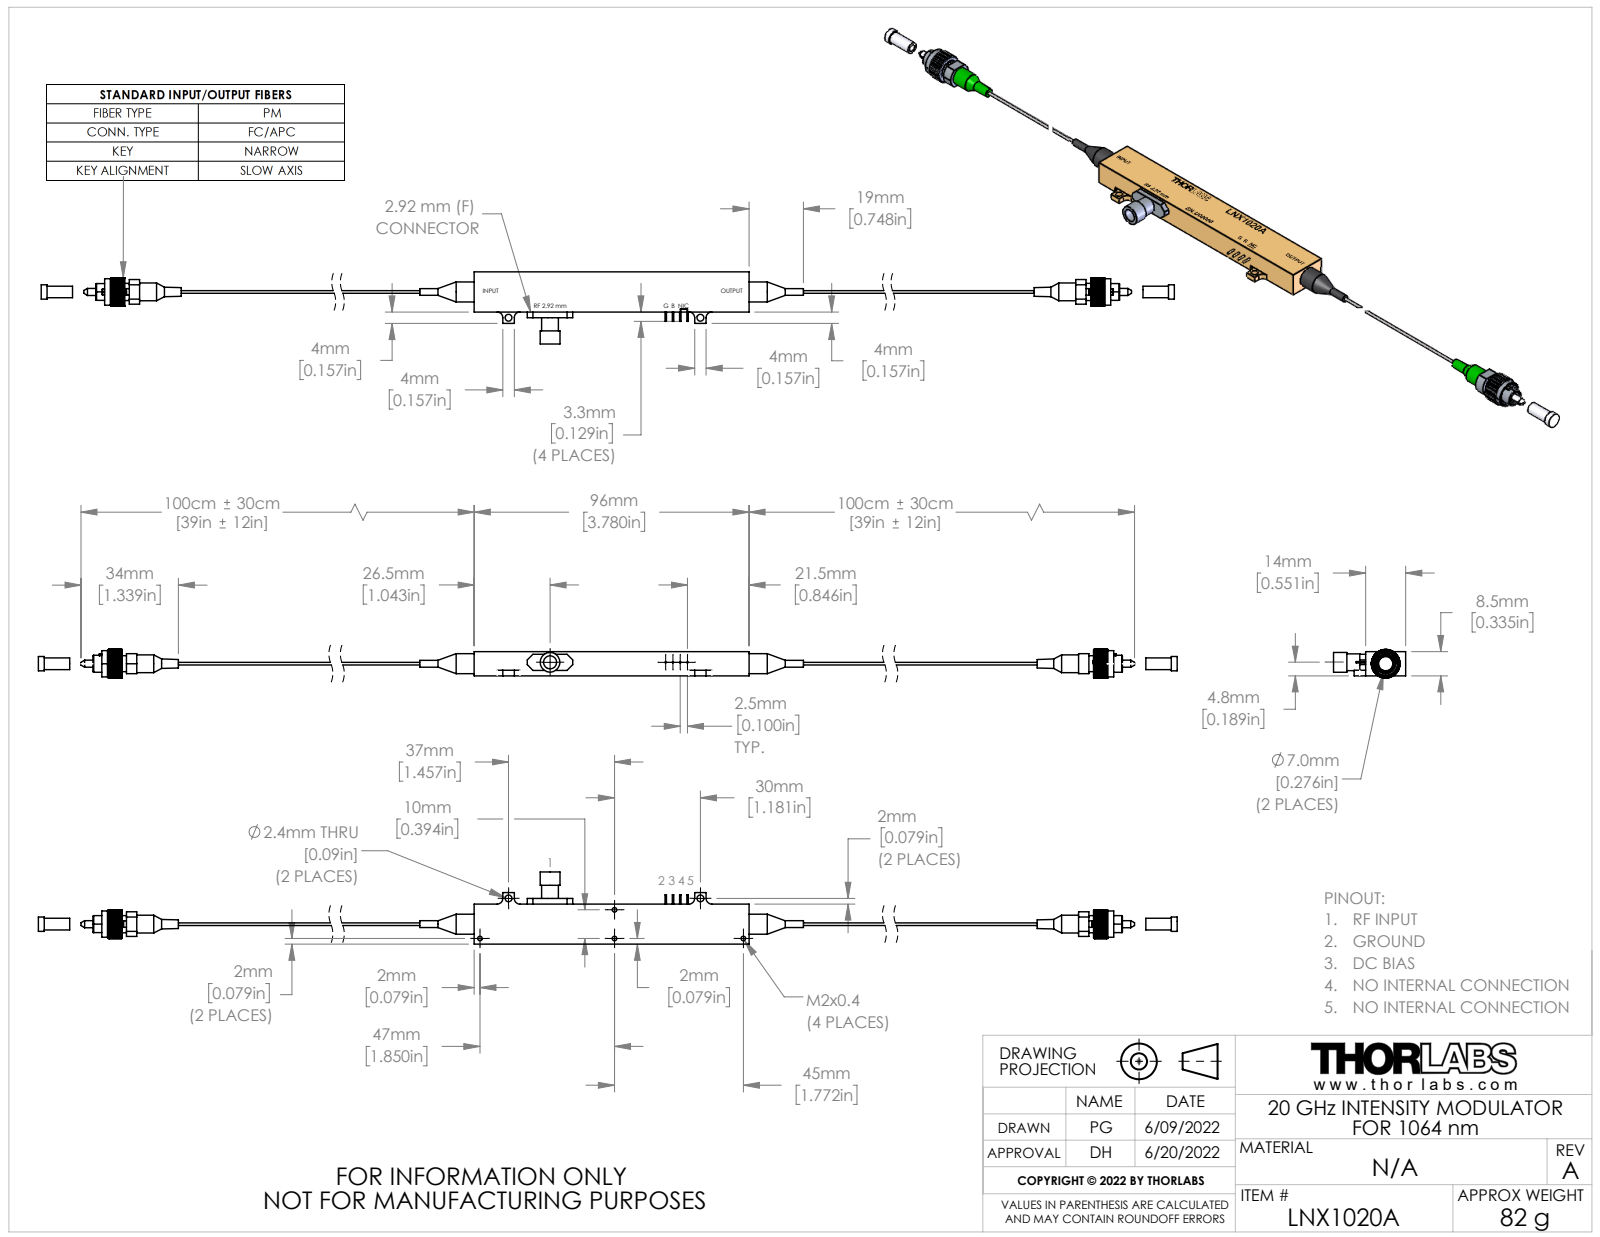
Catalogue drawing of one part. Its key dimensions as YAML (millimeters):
part_name: "LNX1020A; OHW-00233_LNX1020A; Thorlabs CAPF; LNX PC-APC Fiber Connector"
step_written_by: "SolidWorks 2018 (AUTOMOTIVE_DESIGN)"
units: millimeters
bodies: {solids: 13, faces: 3161, planar: 539, cylindrical: 892, other: 1730}
overall_size: [472.7, 25.2, 10]
volume: 14400
surface_area: 11010
round_holes:
  - {diameter: 1.6, count: 4}
  - {diameter: 2.4, count: 2}
  - {diameter: 1.1, count: 1}
  - {diameter: 2.5, count: 1}
  - {diameter: 2.7, count: 1}
  - {diameter: 3.2, count: 1}
  - {diameter: 3.8, count: 1}
  - {diameter: 4.3, count: 1}
  - {diameter: 4.4, count: 1}
  - {diameter: 4.6, count: 1}
  - {diameter: 5, count: 1}
  - {diameter: 5.5, count: 1}
round_bosses_or_shafts:
  - {diameter: 0.5, count: 4}
  - {diameter: 6.9, count: 2}
  - {diameter: 9.2, count: 1}
  - {diameter: 7, count: 1}
  - {diameter: 6.2, count: 1}
  - {diameter: 6, count: 1}
  - {diameter: 5.9, count: 1}
  - {diameter: 5.8, count: 1}
partial_cylinders:
  - {radius: 2, count: 4}
  - {radius: 4.3, count: 1}
  - {radius: 5, count: 1}
face_to_face_distances: [8.5, 14, 154, 250, 2, 96, 4.9, 0.8, 7.7, 3.6]
hole_center_spacings: [10, 17.2, 20.5, 30.3, 33.1, 37.2, 39.5, 45]
